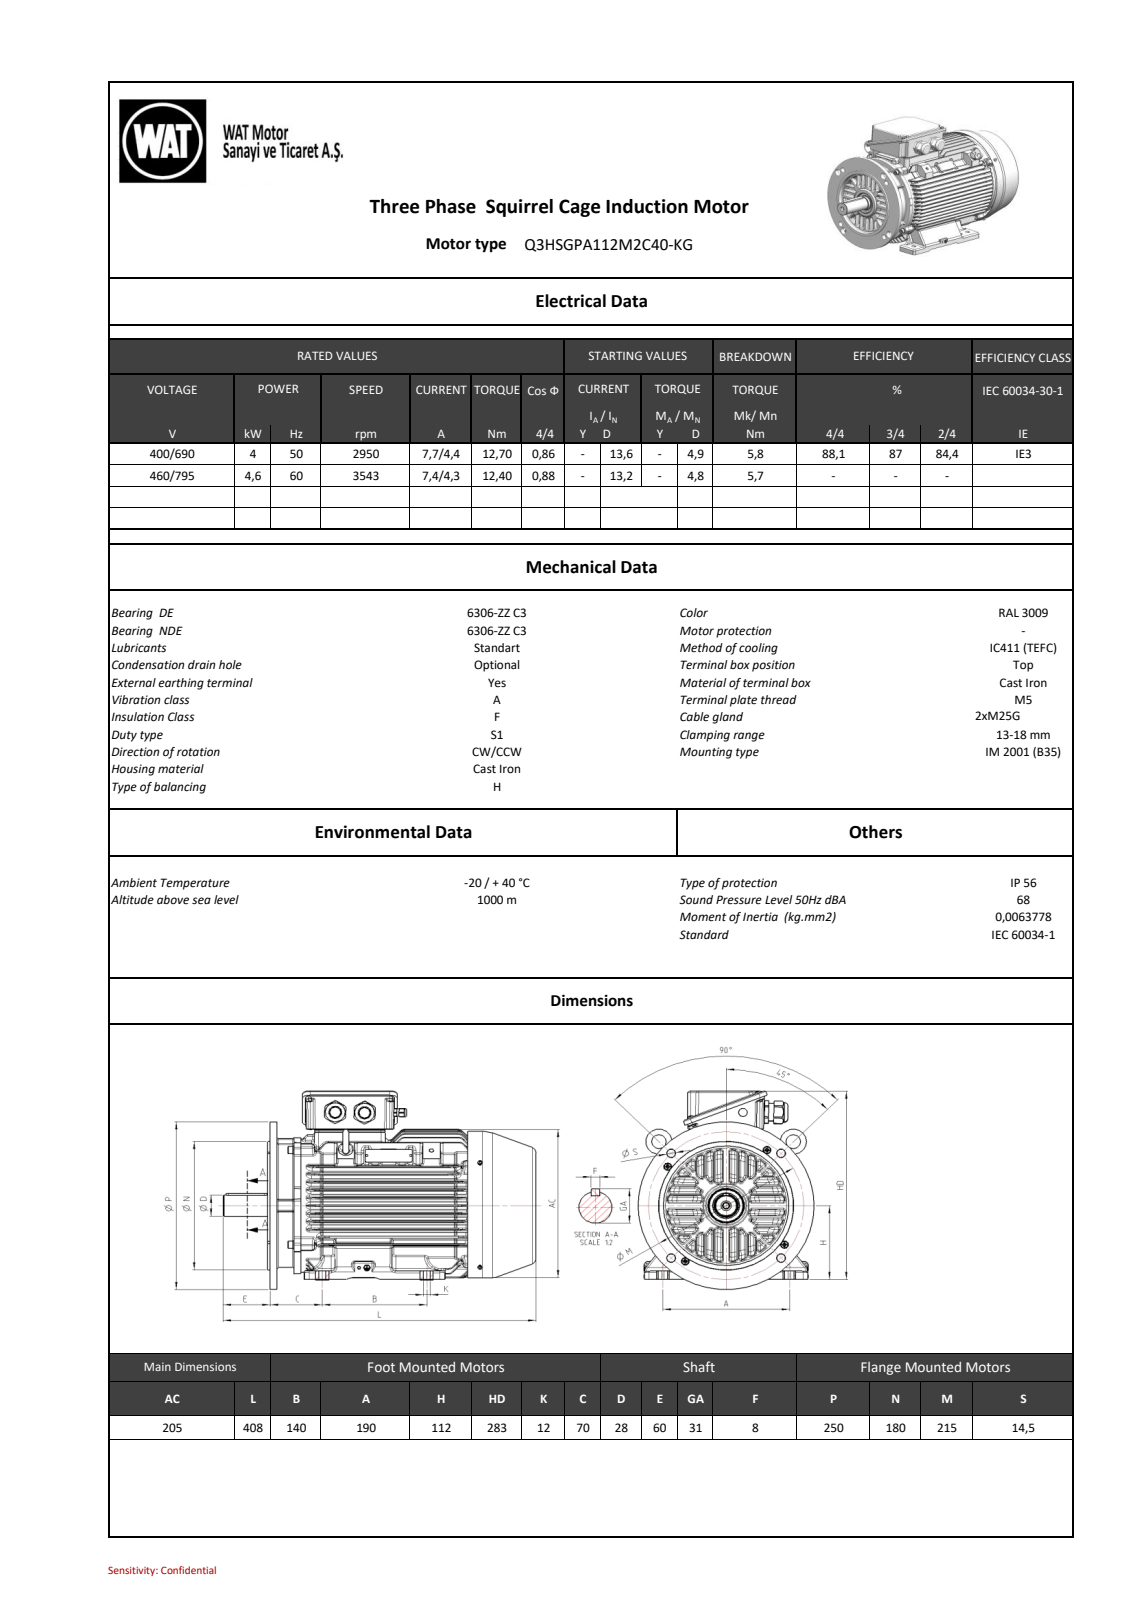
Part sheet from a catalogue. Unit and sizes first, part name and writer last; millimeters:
Units: millimetres
Overall size (bounding box): 408 × 295.48 × 250
Round holes (diameter × count): ⌀5 ×7, ⌀11 ×4, ⌀2.5 ×2, ⌀6.8 ×2, ⌀4.2 ×1, ⌀6.5 ×1, ⌀6.6 ×1, ⌀8.5 ×1, ⌀10 ×1, ⌀10.5 ×1, ⌀43.4 ×1, ⌀43.6 ×1
Round bosses / shafts (diameter × count): ⌀10 ×4, ⌀8.65 ×4, ⌀8 ×4, ⌀4 ×3, ⌀31.6 ×2, ⌀20 ×2, ⌀250 ×1, ⌀200 ×1
Partial cylindrical surfaces — rounded edges, fillets, slot ends (radius × count): R4 ×279, R3 ×151, R1.5 ×130, R2 ×35, R5 ×28, R6 ×28, R1.8 ×23, R1 ×22
Main face-to-face distances: 13.53, 13.62, 27.15, 40.84, 27.31, 13.69, 78.83, 65.21, 51.68, 13.78
Hole centre spacings: 89.5, 126.57, 31.07, 102.68, 146.62, 176.28, 179, 27.5
Bodies: 0 solids, 5106 faces (911 planar, 1330 cylindrical, 2865 other)
Part name (STEP PRODUCT): 26000A30F4D8romj
STEP written by: SIEMENS PLM Software NX 11.0 (AUTOMOTIVE_DESIGN)
